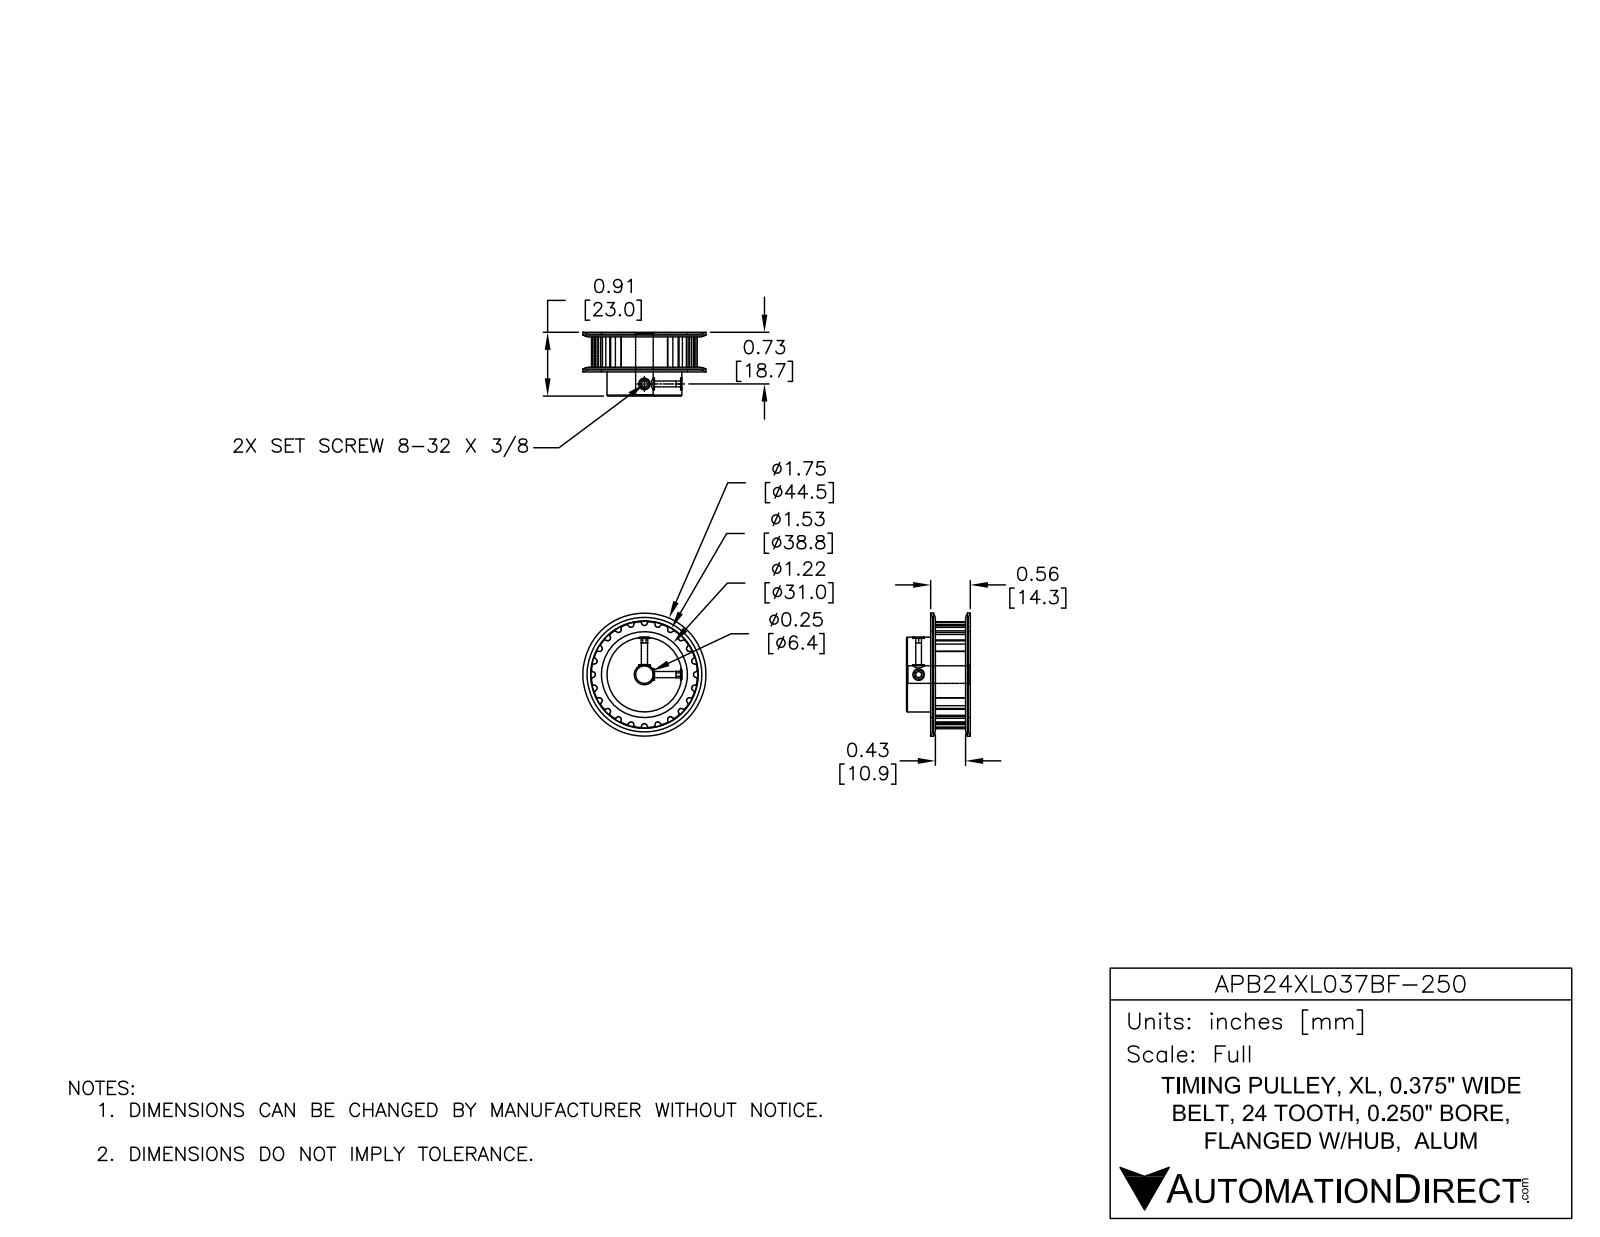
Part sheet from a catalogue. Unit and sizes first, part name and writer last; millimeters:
Units: millimetres
Overall size (bounding box): 44.5 × 44.5 × 23
Round holes (diameter × count): ⌀2.2 ×2, ⌀6.4 ×1
Round bosses / shafts (diameter × count): ⌀27 ×1
Partial cylindrical surfaces — rounded edges, fillets, slot ends (radius × count): R0.4 ×96, R17.8 ×1
Main face-to-face distances: 12.6, 0.8, 13.4, 23, 22.2, 9.6, 38.3, 13.9, 1.7, 0.8
Volume: 19 600 mm³ · Surface area: 7 342 mm²
Bodies: 1 solid, 246 faces (78 planar, 146 cylindrical, 22 other)
Part name (STEP PRODUCT): APB24XL037BF-250
STEP written by: SolidWorks 2014 (AUTOMOTIVE_DESIGN)
